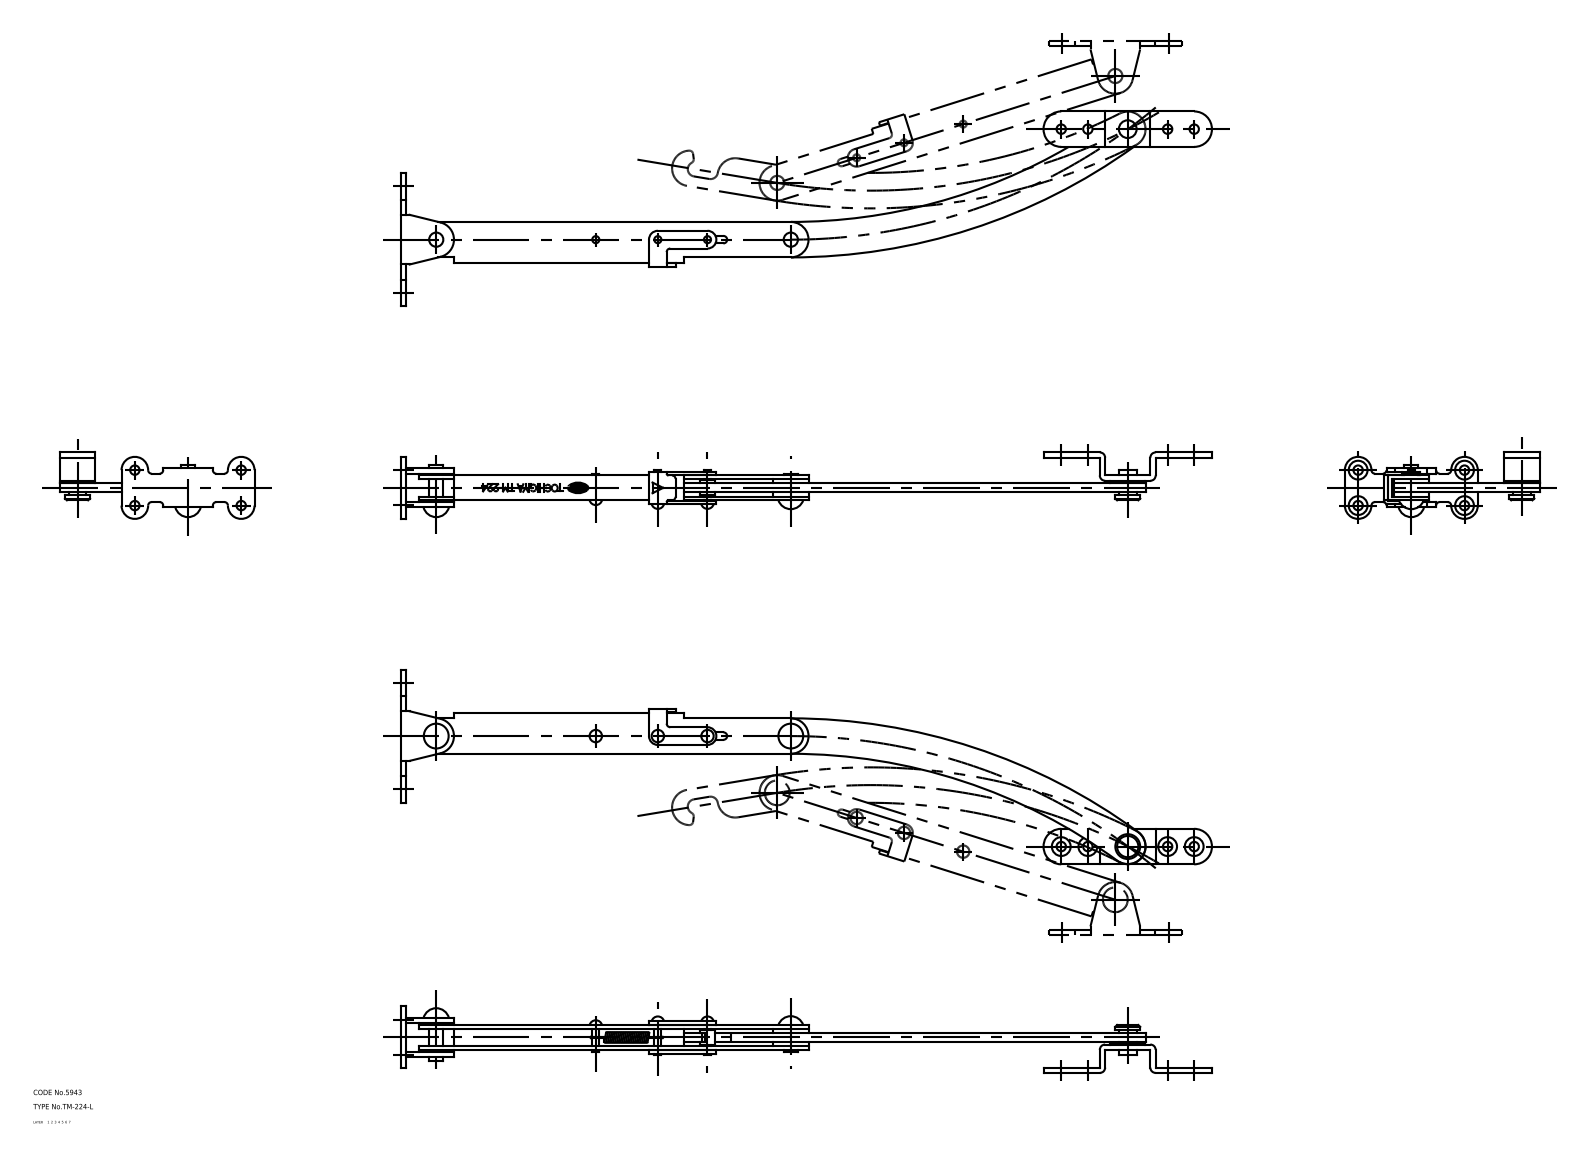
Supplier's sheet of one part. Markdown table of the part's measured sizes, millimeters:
| quantity | value |
| --- | --- |
| part name | spacer_B; bracket_B; TM_224_L; rivet_C (+8 more) |
| STEP written by | SolidWorks 2015 (AUTOMOTIVE_DESIGN) |
| units | millimeters |
| bodies | 18 solids, 314 faces (99 planar, 149 cylindrical, 66 other) |
| overall size | 457.54 × 109.83 × 37.5 |
| volume | 69 529 mm³ |
| surface area | 58 726 mm² |
| round holes (diameter × count) | 5.3 × 8, 4 × 2, 4.1 × 2, 8 × 2, 8.1 × 2, 10 × 1 |
| round bosses / shafts (diameter × count) | 20 × 3, 14 × 1, 8 × 1, 4 × 1 |
| partial cylindrical surfaces (radius × count) | 2 × 15, 3 × 6, 10 × 5, 7.5 × 4, 0.1 × 2, 1 × 2, 2.1 × 2, 4.1 × 2 |
| main face-to-face distances | 2, 12, 4.5, 9.5, 7.5, 2.5, 3, 5, 10, 14 |
| hole center spacings | 60, 15, 20, 22.5, 37.5, 63.25, 75, 200 |
